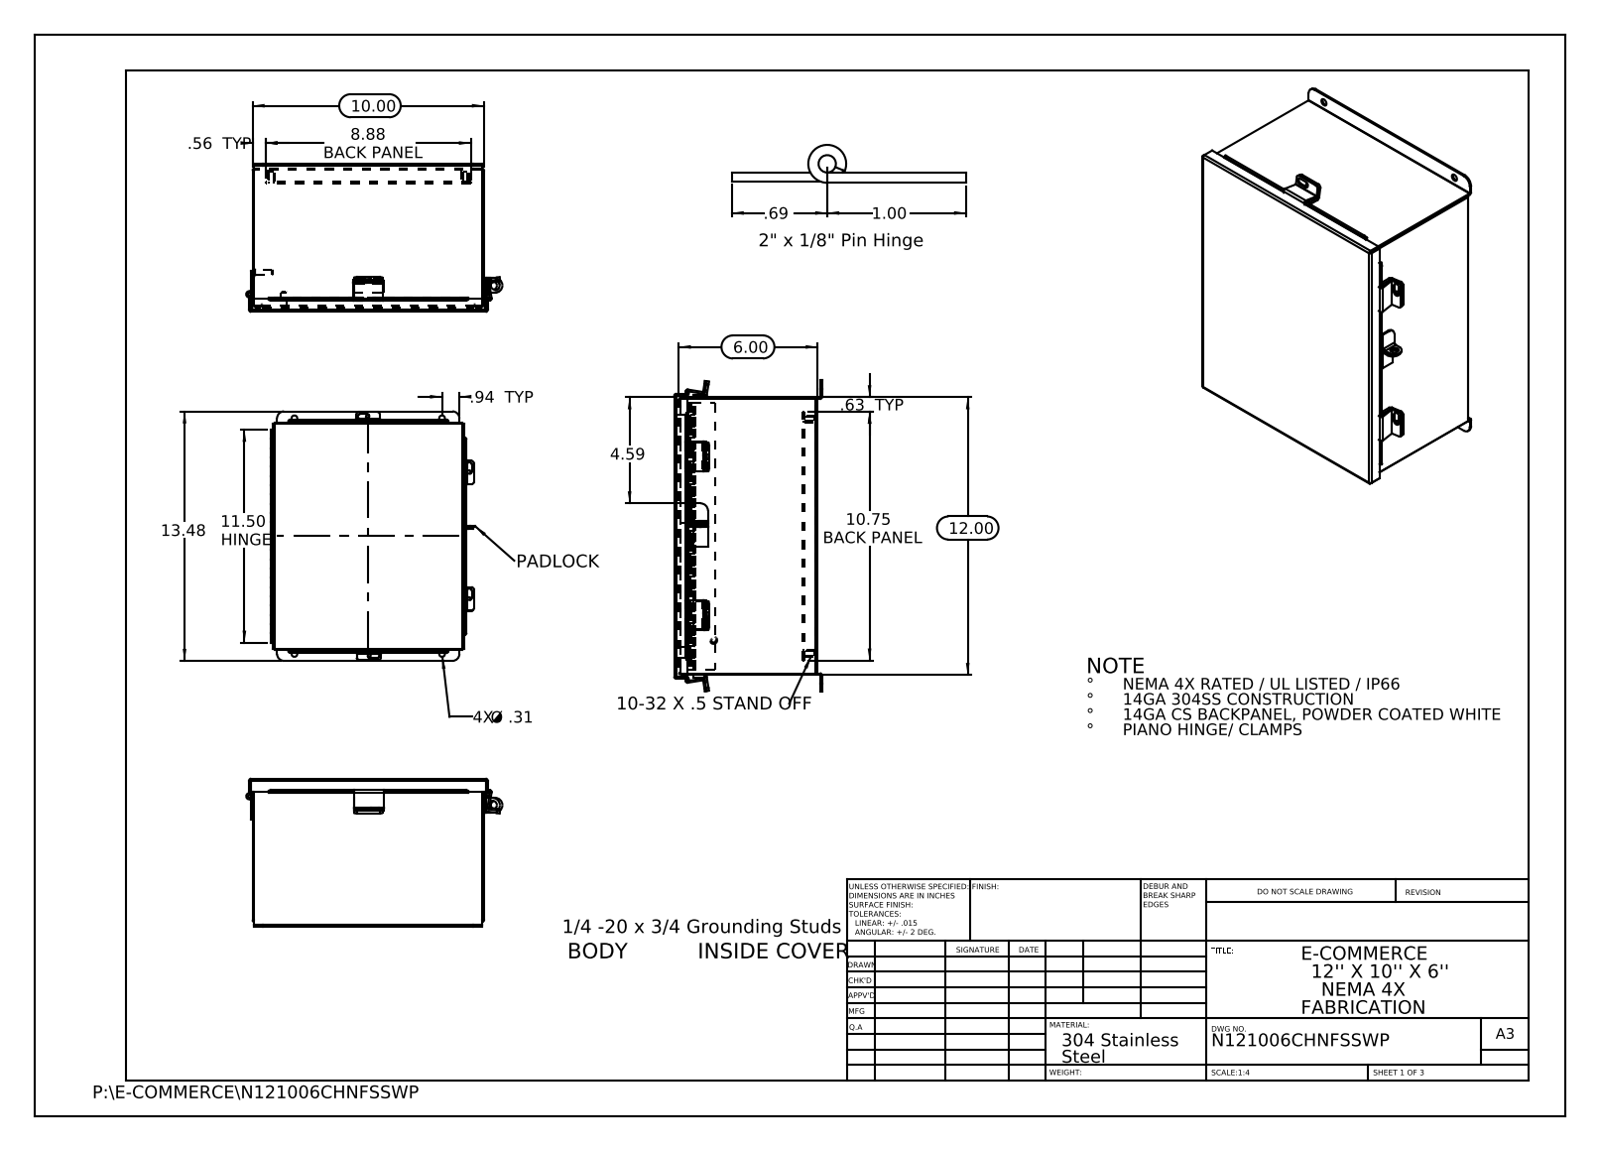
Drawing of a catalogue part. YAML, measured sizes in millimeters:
part_name: "N121006CHNFSSWP JIC Enclosure Template; N121006CHNFSSWP Hinge Body Side; HW-CLH-JH-20104; N121006CHNFSSWP (+8 more)"
step_written_by: "SolidWorks 2013 (CONFIG_CONTROL_DESIGN)"
units: millimeters
bodies: {solids: 23, faces: 702, planar: 435, cylindrical: 247, other: 20}
overall_size: [342.3, 281.2, 162.3]
volume: 849800
surface_area: 913500
round_holes:
  - {diameter: 6.4, count: 8}
  - {diameter: 4.7, count: 4}
  - {diameter: 7.9, count: 4}
  - {diameter: 3.2, count: 1}
  - {diameter: 3.2, count: 1}
  - {diameter: 9.5, count: 1}
  - {diameter: 9.5, count: 1}
round_bosses_or_shafts:
  - {diameter: 8, count: 4}
  - {diameter: 8, count: 2}
  - {diameter: 6, count: 2}
  - {diameter: 6.9, count: 1}
  - {diameter: 6.4, count: 1}
partial_cylinders:
  - {radius: 3.2, count: 14}
  - {radius: 0.3, count: 13}
  - {radius: 0.2, count: 12}
  - {radius: 2.2, count: 12}
  - {radius: 3.4, count: 8}
  - {radius: 2.1, count: 6}
  - {radius: 2.5, count: 6}
  - {radius: 9.5, count: 4}
face_to_face_distances: [1.9, 155.7, 252.1, 302.9, 153.7, 157.6, 1.9, 14.6, 12.7, 141]
hole_center_spacings: [33.4, 210.3, 290.3, 356.9, 202.6, 212.7, 257.2, 323.2]
